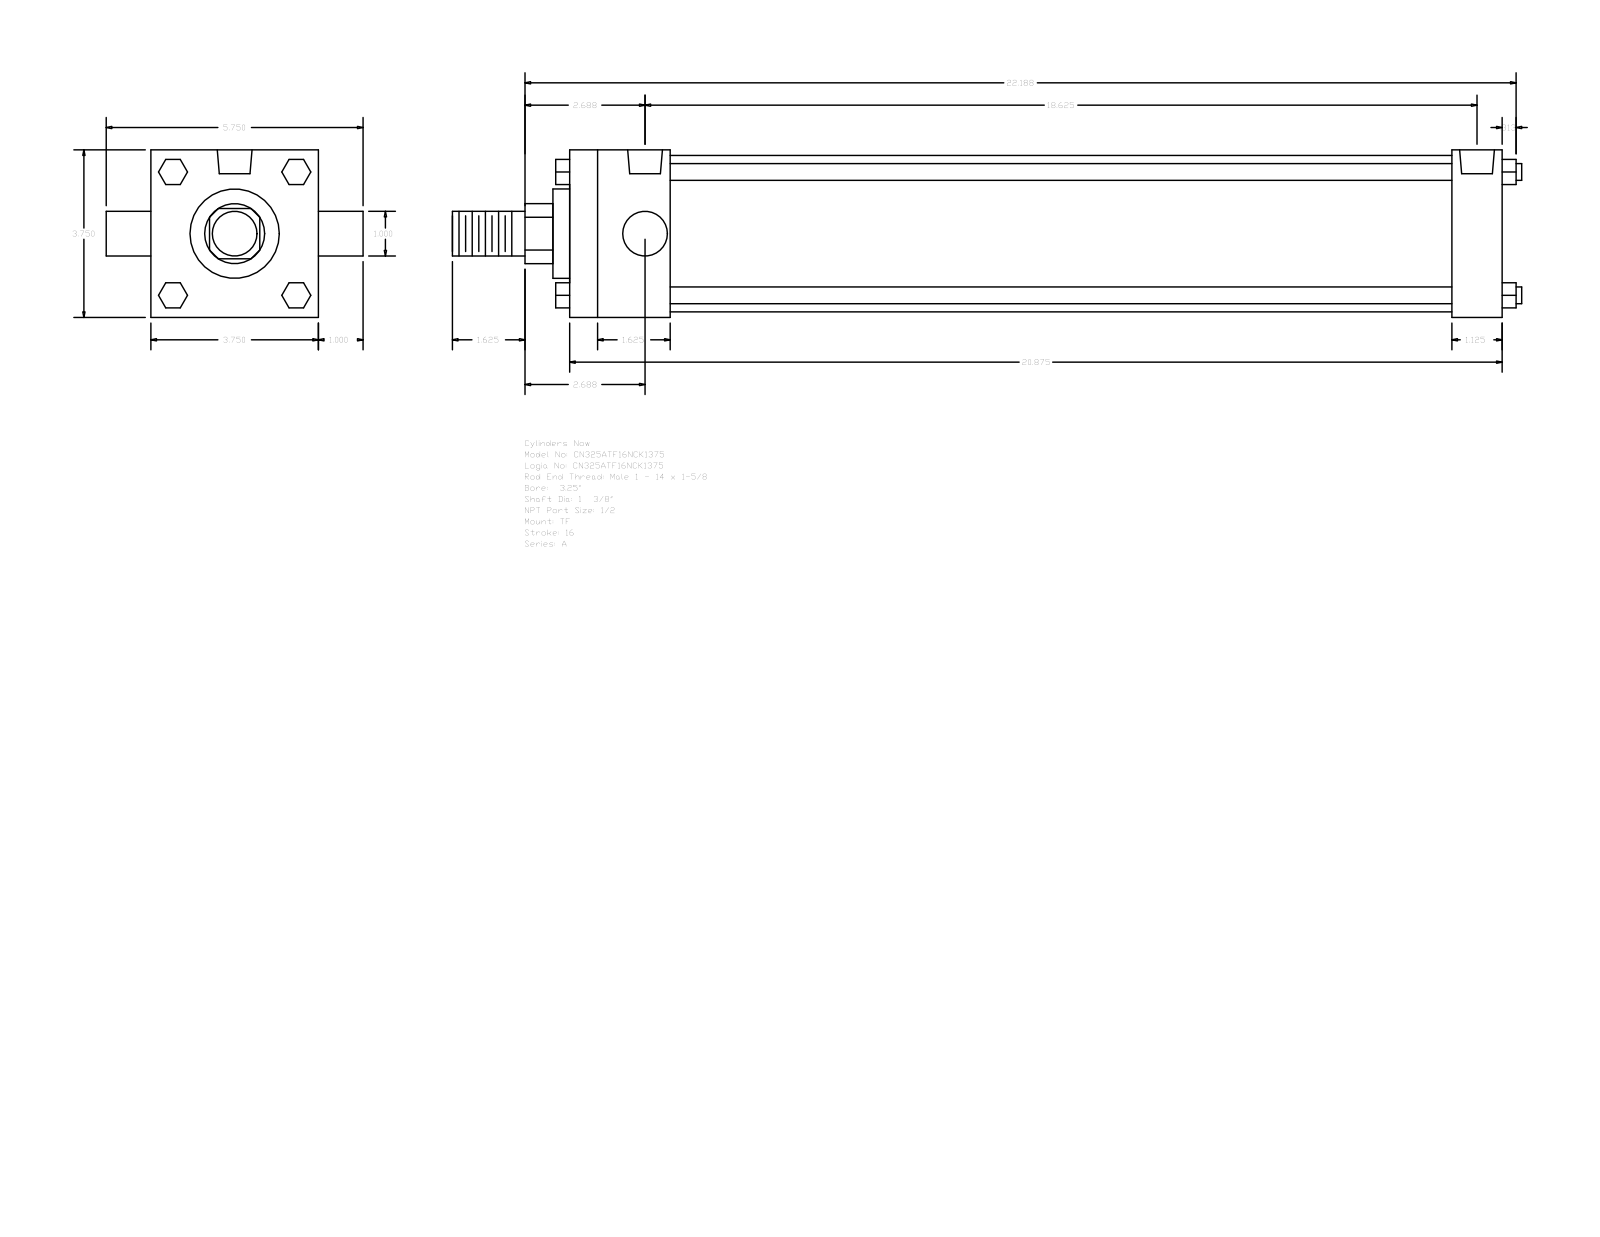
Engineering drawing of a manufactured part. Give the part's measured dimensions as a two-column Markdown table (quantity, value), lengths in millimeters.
| quantity | value |
| --- | --- |
| part name | A_TF__0325_1.375 |
| STEP written by | GSSL Pune (CONFIG_CONTROL_DESIGN) |
| units | millimeters |
| bodies | 0 solids, 120 faces (92 planar, 28 cylindrical, 0 other) |
| overall size | 608.01 × 146.05 × 95.25 |
| round holes (diameter × count) | 8.73 × 3, 19.77 × 2 |
| round bosses / shafts (diameter × count) | 9.53 × 4, 25.4 × 2, 88.9 × 1, 50.8 × 1, 34.92 × 1 |
| partial cylindrical surfaces (radius × count) | 17.06 × 1 |
| main face-to-face distances | 95.24, 530.22, 57.15, 501.65, 444.5, 473.07, 28.57, 66.67, 9.52, 511.17 |
| hole center spacings | 3.18, 469.9, 466.72, 473.08 |
